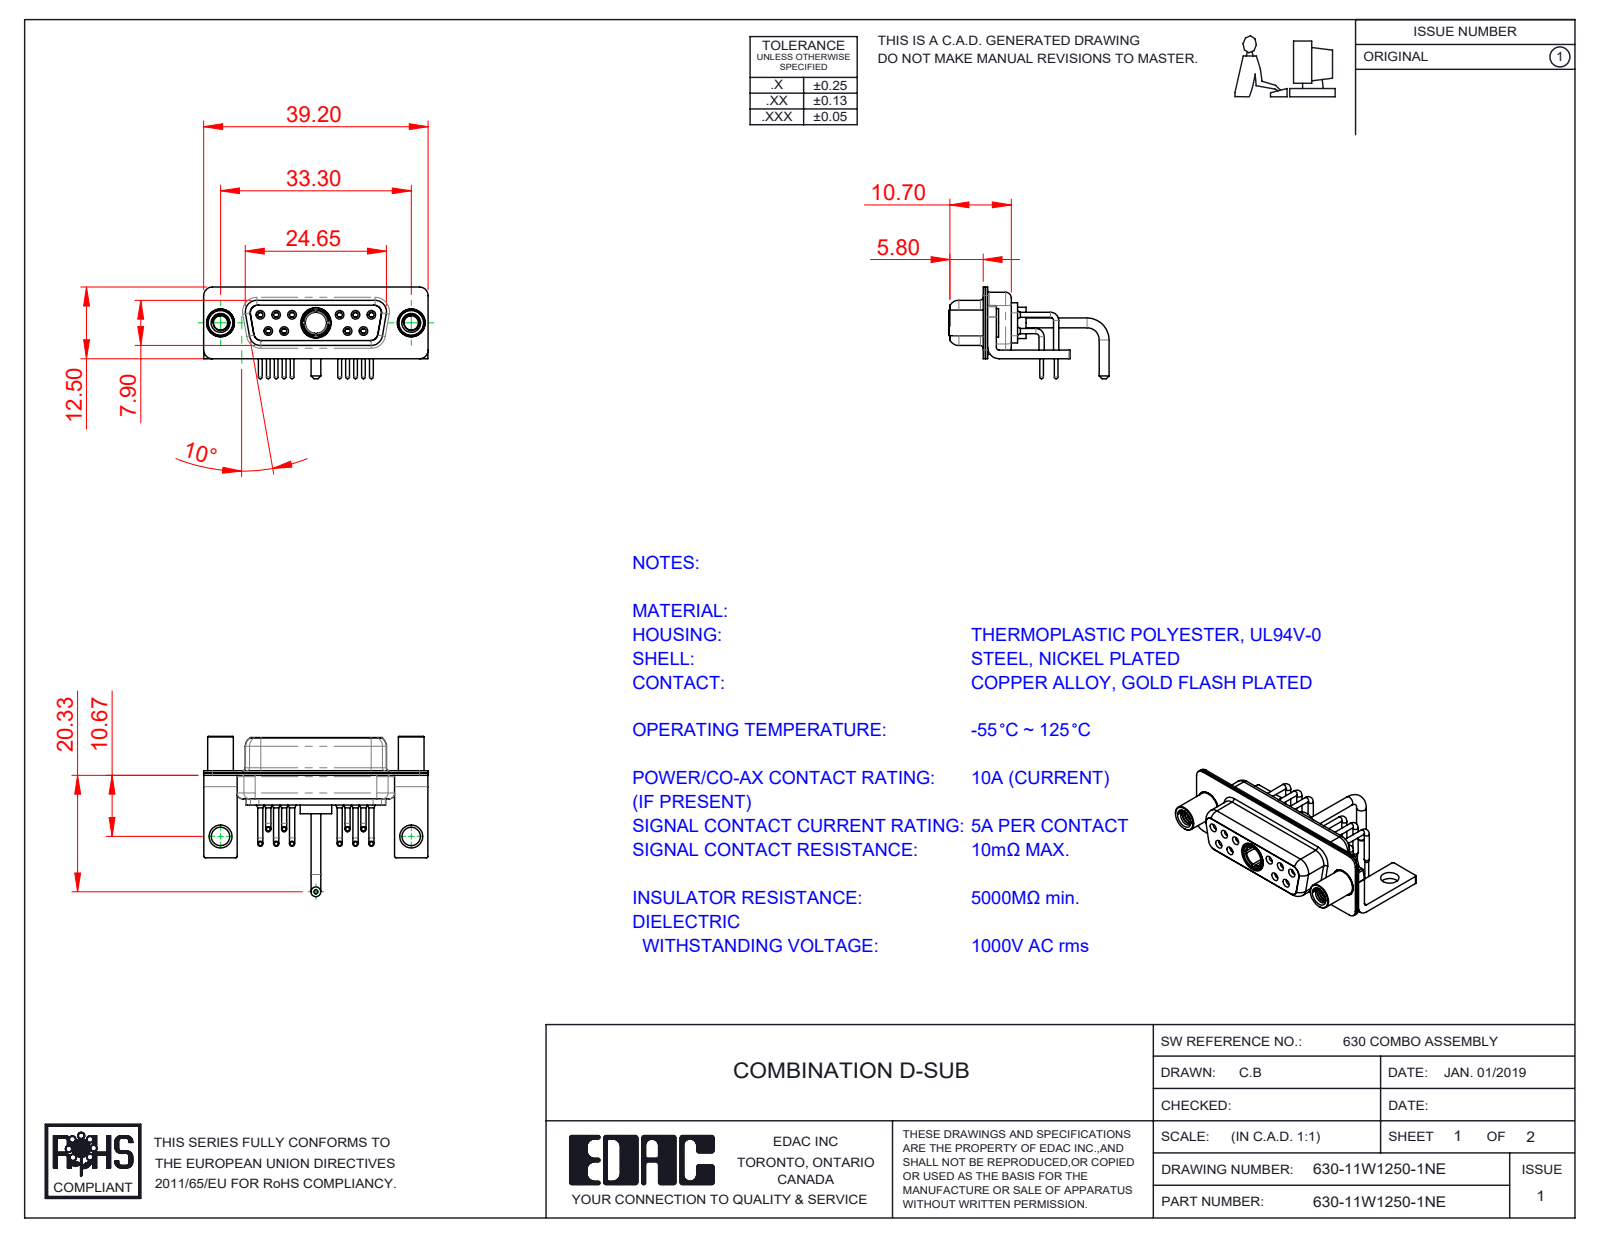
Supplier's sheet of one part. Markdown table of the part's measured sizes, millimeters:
| quantity | value |
| --- | --- |
| part name | 630Combo Contact Row 1; 630-11W1250-1NE; 630Combo Threaded Standoff_D; 630Combo Stabilizer Bracket (+5 more) |
| STEP written by | SolidWorks 2020 (CONFIG_CONTROL_DESIGN) |
| units | millimeters |
| bodies | 19 solids, 985 faces (268 planar, 464 cylindrical, 253 other) |
| overall size | 39.2 × 27.98 × 16 |
| volume | 2 988 mm³ |
| surface area | 7 184 mm² |
| round holes (diameter × count) | 0.9 × 10, 1.1 × 10, 1.5 × 10, 2 × 10, 1.7 × 6, 1.6 × 4, 4.85 × 3, 2.5 × 2, 3.2 × 2, 4 × 2, 4.05 × 2, 3.7 × 1 |
| round bosses / shafts (diameter × count) | 0.9 × 10, 0.65 × 10, 1.6 × 6, 5 × 2, 4.95 × 2, 4.8 × 2, 4.5 × 2, 1.7 × 2 |
| partial cylindrical surfaces (radius × count) | 0.25 × 16, 1.5 × 16, 2 × 13, 1.35 × 12, 1.6 × 8, 0.5 × 5, 0.6 × 4, 0.65 × 4 |
| main face-to-face distances | 0.4, 0.8, 1.4, 0.45, 8.45, 1.5, 1.8, 8.9, 6.2, 2.3 |
| hole center spacings | 3.16, 2.77, 13.85, 11.08, 16.62, 5.03, 5.04, 5.54 |
